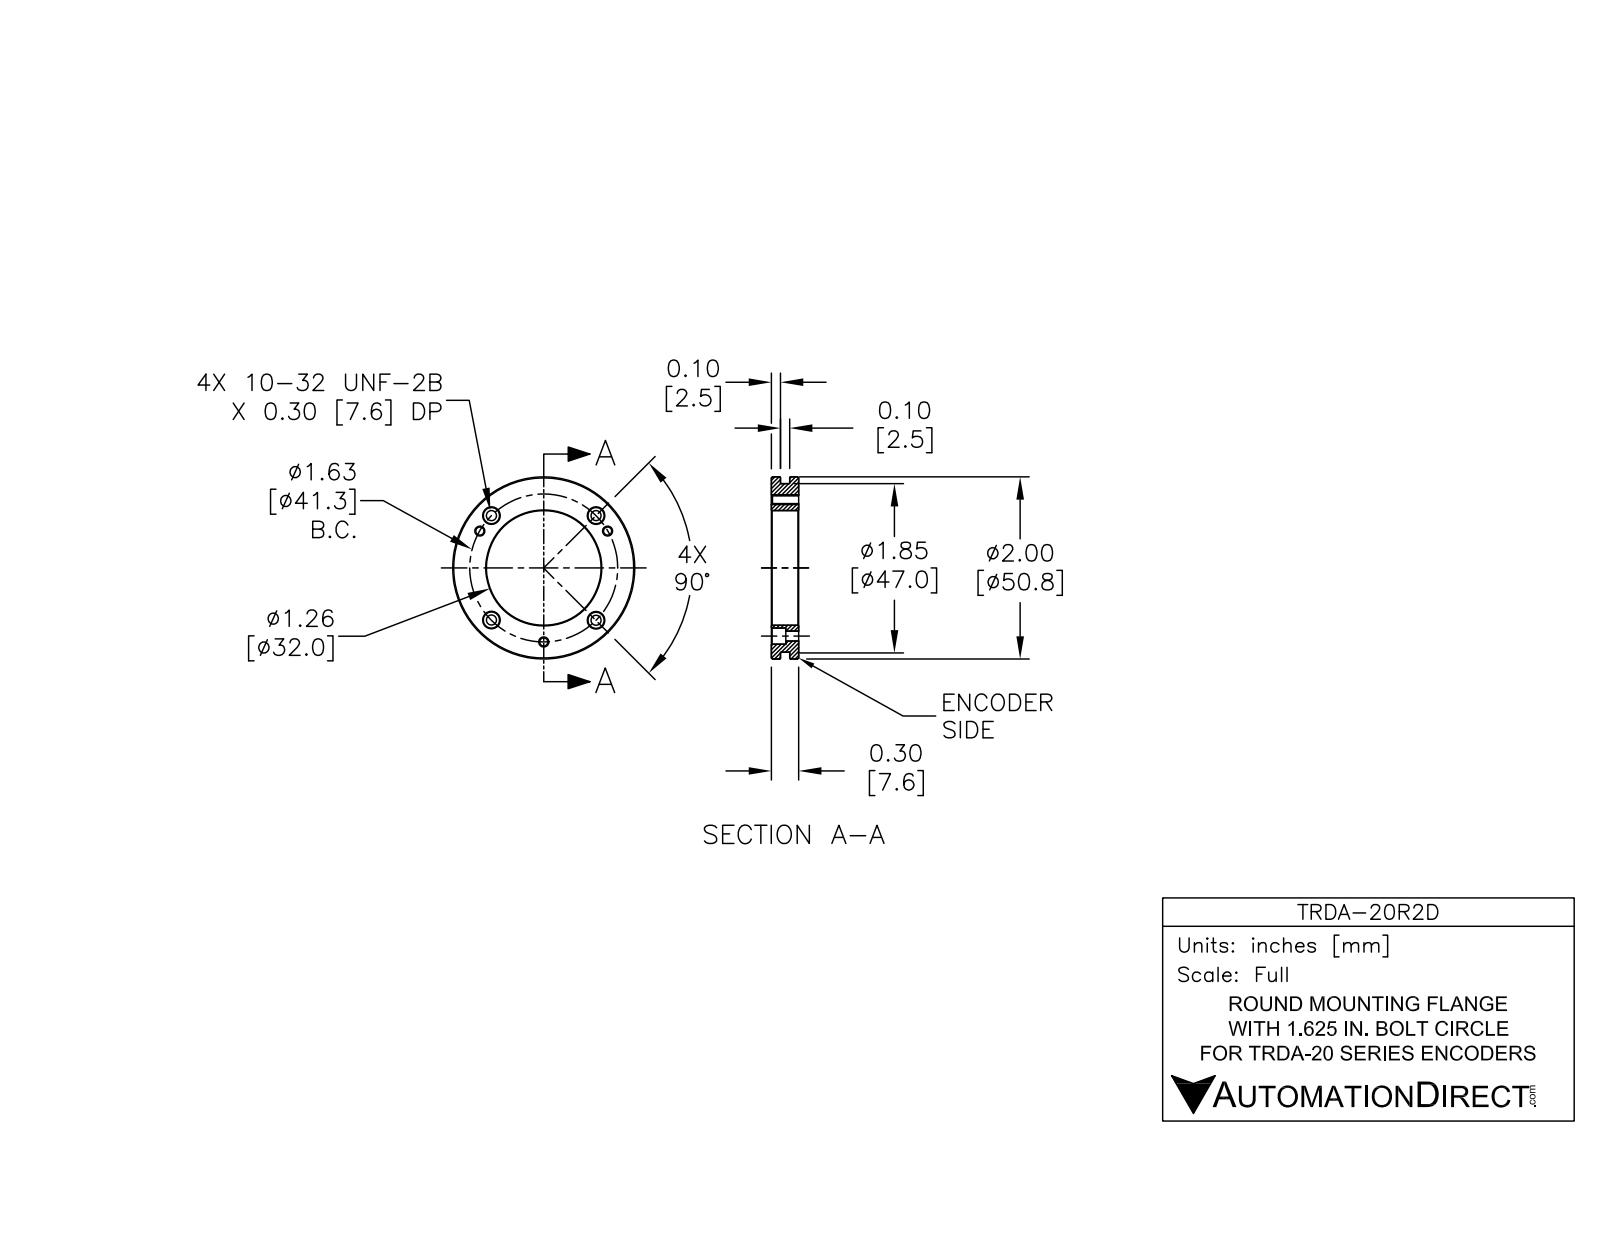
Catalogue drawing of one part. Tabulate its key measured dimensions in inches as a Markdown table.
| quantity | value |
| --- | --- |
| part name | TRDA-20R2D |
| STEP written by | SolidWorks 2017 (AUTOMOTIVE_DESIGN) |
| units | inches |
| bodies | 5 solids, 77 faces (15 planar, 36 cylindrical, 26 other) |
| overall size | 2 × 2 × 0.299 |
| volume | 0.514 in³ |
| surface area | 9.241 in² |
| round holes (diameter × count) | 0.159 × 4, 0.11 × 3, 0.177 × 3, 1.26 × 1 |
| round bosses / shafts (diameter × count) | 0.19 × 4, 2 × 1, 1.85 × 1 |
| main face-to-face distances | 0.299, 0.1, 0.199, 0.099, 0.2, 0.295, 0.196, 0.096, 0.142, 0.043 |
| hole center spacings | 0.812, 1.149, 0.748, 0.213, 0.6, 0.951, 1.238, 1.296 |
